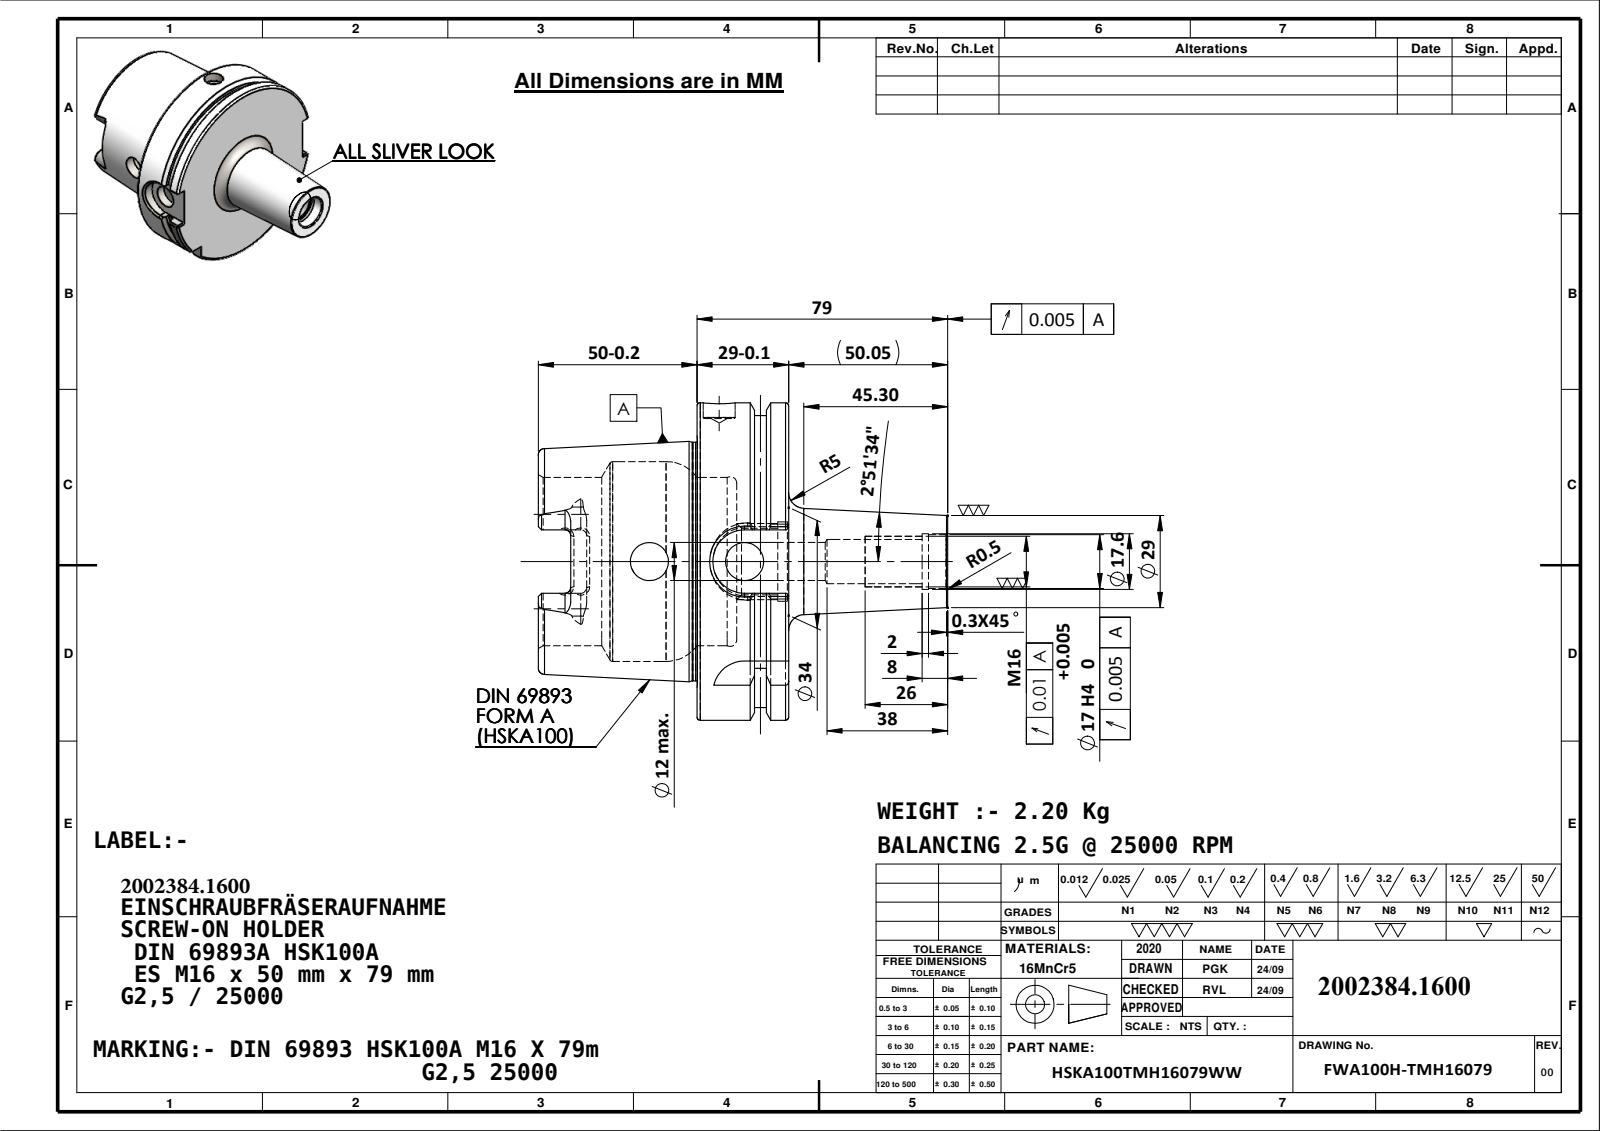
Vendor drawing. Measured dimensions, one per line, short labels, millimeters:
name: 91100A-ES8M16050
written by: SolidWorks 2018 (AUTOMOTIVE_DESIGN)
unit: mm
bodies: 1 solid, 174 faces (50 planar, 52 cylindrical, 72 other)
size: 129 × 100 × 100
volume: 285 472 mm³; area: 56 356 mm²
holes: 3× ⌀12, 1× ⌀10, 1× ⌀14, 1× ⌀17, 1× ⌀17.6, 1× ⌀21, 1× ⌀25, 1× ⌀53, 1× ⌀63
bosses: 1× ⌀100, 1× ⌀92, 1× ⌀75.16
rounds: 6× R1.8, 4× R4.88, 2× R10, 1× R11
face distances: 28.95, 12.5, 16.45, 50, 62.5, 78.95, 71.88, 21.88, 9.38, 7.07
hole spacings: 30
